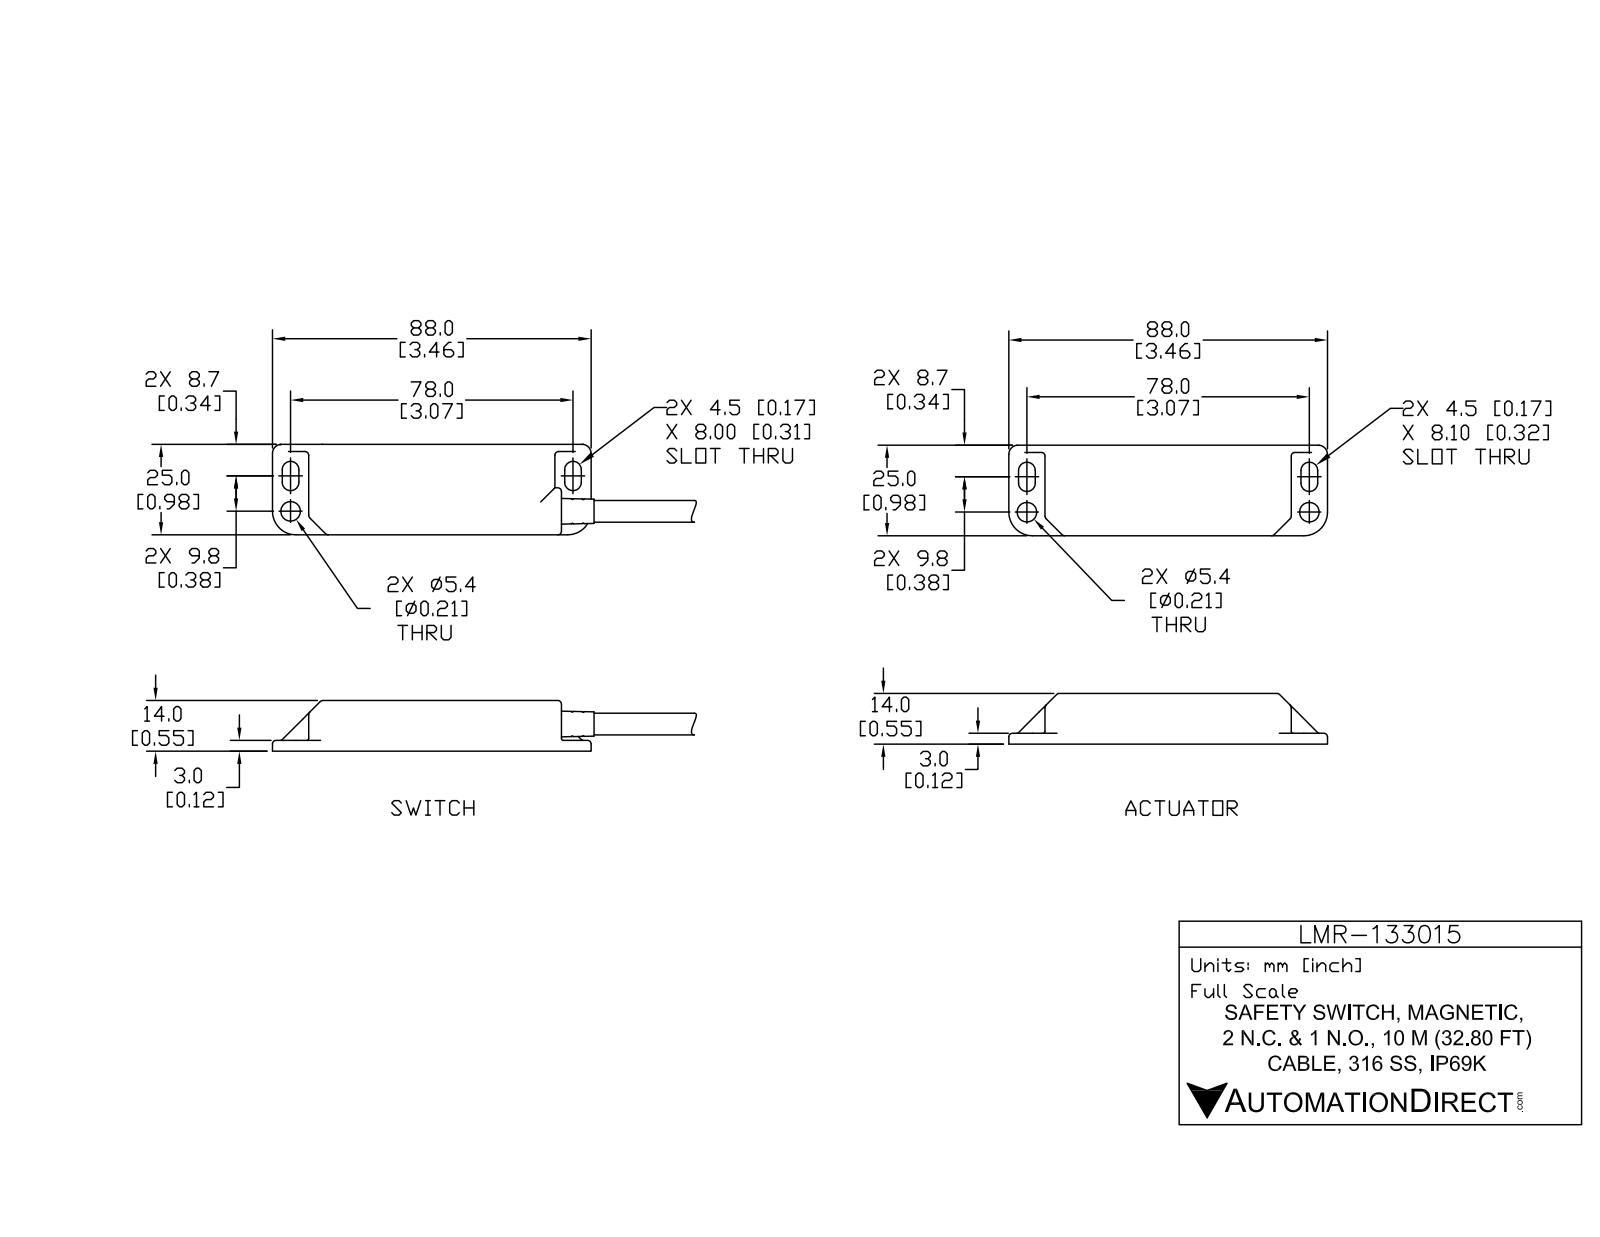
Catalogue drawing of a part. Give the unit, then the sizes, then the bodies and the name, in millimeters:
Units: millimetres
Overall size (bounding box): 233 × 51 × 14
Round holes (diameter × count): ⌀5 ×4, ⌀5.4 ×4, ⌀5.9 ×1, ⌀7.2 ×1
Round bosses / shafts (diameter × count): ⌀2 ×4, ⌀4.9 ×2, ⌀3.4 ×2, ⌀8.6 ×1, ⌀7.6 ×1, ⌀7.1 ×1, ⌀6 ×1
Partial cylindrical surfaces — rounded edges, fillets, slot ends (radius × count): R0.5 ×95, R1 ×45, R2.3 ×8, R2.5 ×4, R6.5 ×4, R4.9 ×1
Main face-to-face distances: 1.7, 1.4, 13.8, 26, 12.1, 12.4, 10.7, 23.3, 2.7, 1
Hole centre spacings: 17, 29.8, 30, 31.6, 38, 42.8, 46.1, 48.4
Volume: 27 190 mm³ · Surface area: 29 890 mm²
Bodies: 10 solids, 676 faces (194 planar, 244 cylindrical, 238 other)
Part name (STEP PRODUCT): LMR-133015; LMR-133015_2; LMR-133015_1
STEP written by: SolidWorks 2017 (AUTOMOTIVE_DESIGN)
